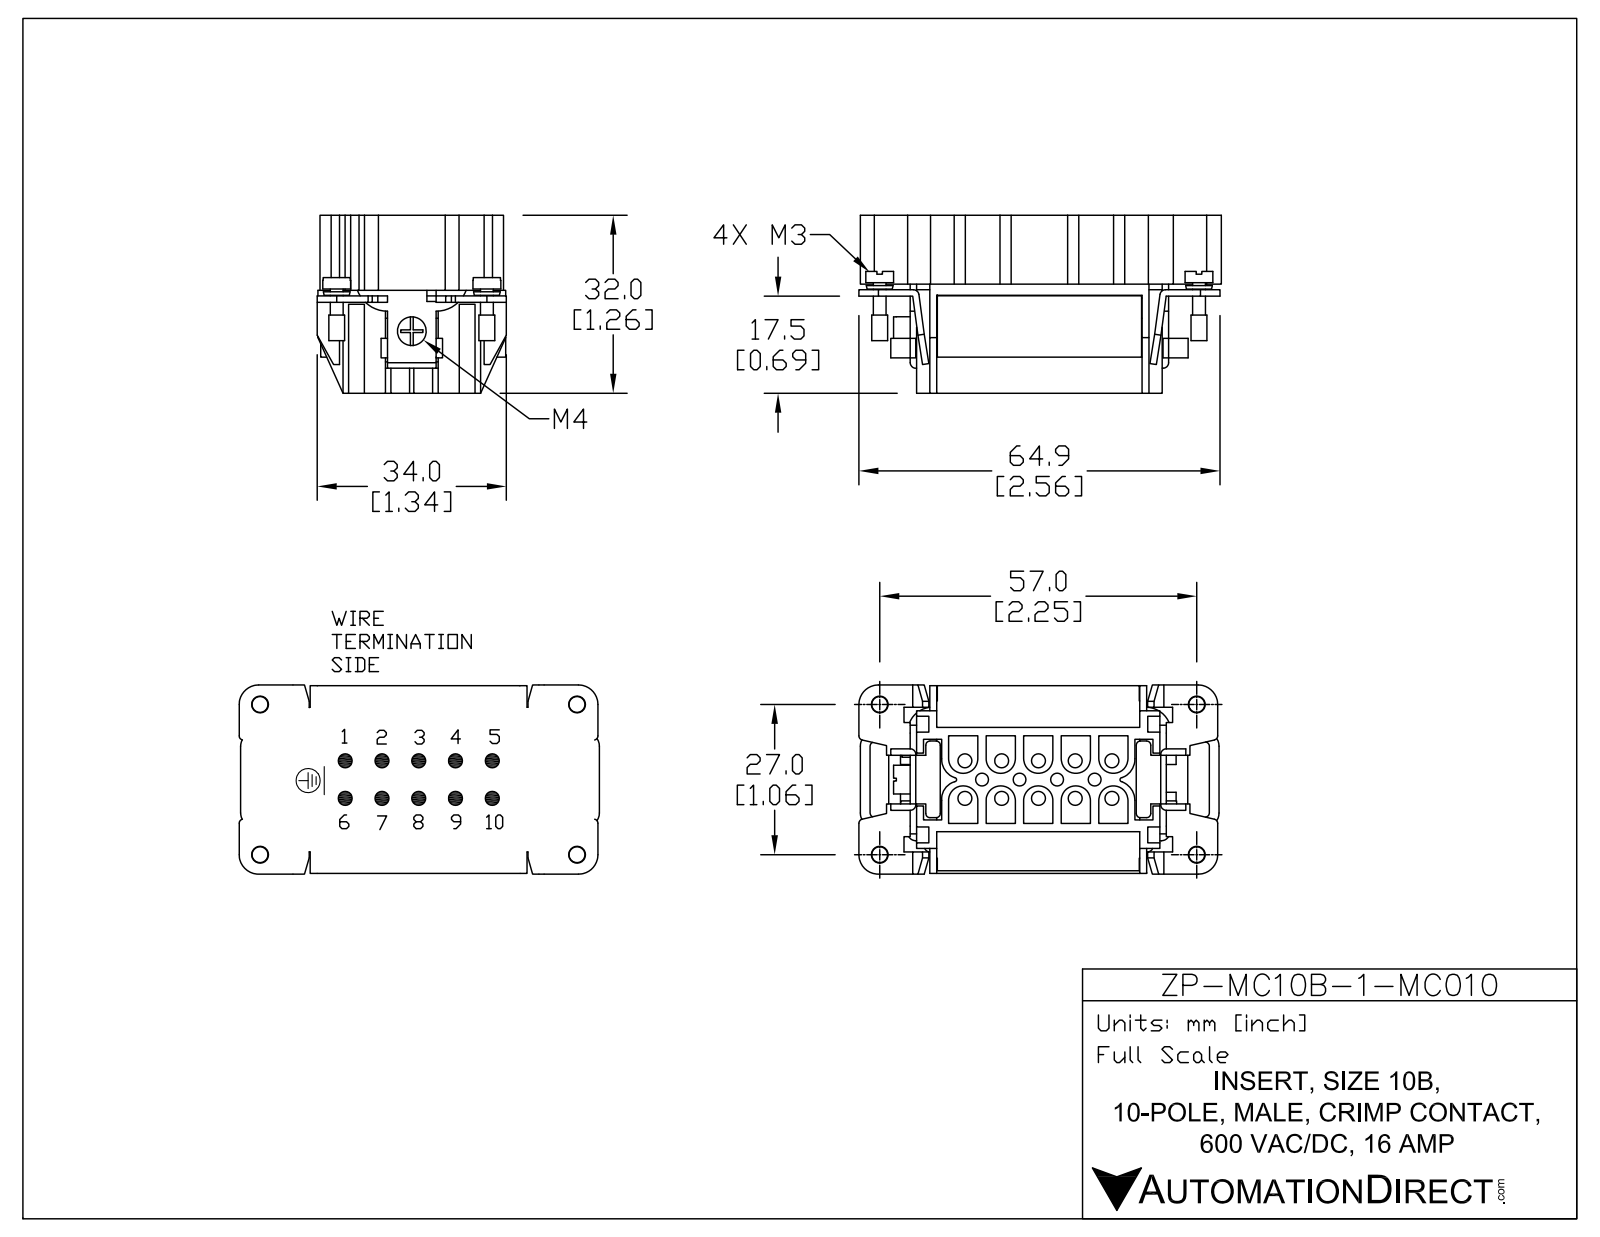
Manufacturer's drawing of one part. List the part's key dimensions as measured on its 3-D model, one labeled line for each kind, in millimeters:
Part name (STEP PRODUCT): ZP-10B-10-MC-INSERT
STEP written by: SolidWorks 2011 (AUTOMOTIVE_DESIGN)
Units: millimetres
Bodies: 6 solids, 595 faces (450 planar, 141 cylindrical, 4 other)
Overall size (bounding box): 64.76 × 34 × 32
Volume: 24 896 mm³ · Surface area: 20 292 mm²
Round holes (diameter × count): ⌀2.5 ×10, ⌀2.3 ×4, ⌀3.01 ×4, ⌀3 ×1
Round bosses / shafts (diameter × count): ⌀5.5 ×10, ⌀5 ×4, ⌀2.85 ×4, ⌀2.3 ×4, ⌀5.17 ×1
Partial cylindrical surfaces — rounded edges, fillets, slot ends (radius × count): R0.75 ×24, R1 ×12, R2.62 ×10, R2.62 ×10, R0.25 ×6, R2 ×6, R2.5 ×4, R3.5 ×4
Main face-to-face distances: 1.75, 1.15, 12, 1, 4.5, 3.62, 24.25, 5.13, 3.38, 1.25
Hole centre spacings: 6.61, 6.75, 9.45, 13.22, 14.84, 19.83, 20.95, 22.79
